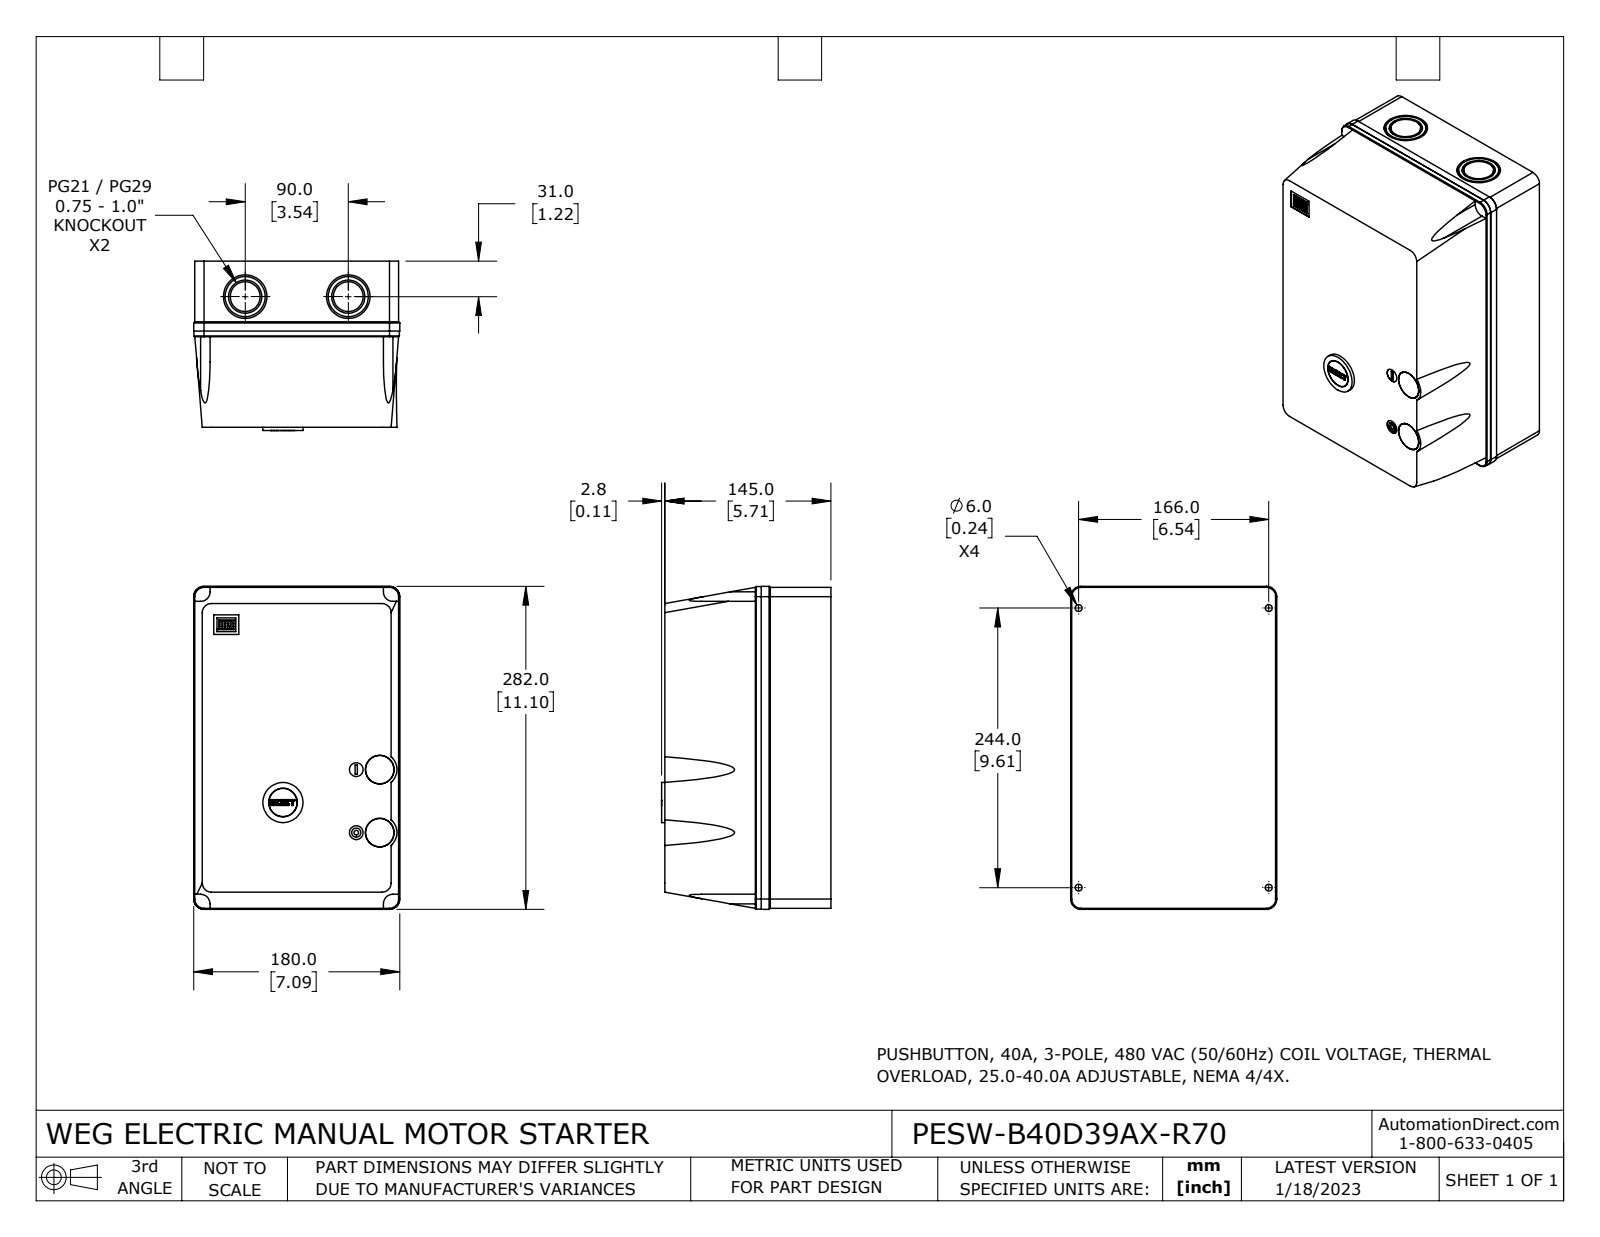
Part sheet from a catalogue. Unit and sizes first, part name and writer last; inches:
Units: inches
Overall size (bounding box): 11.102 × 7.087 × 5.823
Round holes (diameter × count): ⌀0.236 ×4, ⌀0.984 ×3, ⌀0.472 ×2, ⌀1.142 ×2, ⌀1.496 ×2, ⌀0.157 ×1, ⌀1.201 ×1
Round bosses / shafts (diameter × count): ⌀1.378 ×3, ⌀1.024 ×2, ⌀0.976 ×2, ⌀1.193 ×1, ⌀0.969 ×1, ⌀0.551 ×1, ⌀0.315 ×1
Partial cylindrical surfaces — rounded edges, fillets, slot ends (radius × count): R0.004 ×34, R0.315 ×4, R0.327 ×4, R0.343 ×4, R0.354 ×4, R0.063 ×1
Main face-to-face distances: 5.709, 7.008, 11.024, 0.039, 0.028, 7.047, 7.075, 7.035, 11.063, 7.087
Hole centre spacings: 0.807, 2.165, 2.311, 6.535, 9.606, 11.619, 1.935, 2.25
Volume: 428 in³ · Surface area: 360 in²
Bodies: 3 solids, 286 faces (130 planar, 144 cylindrical, 12 other)
Part name (STEP PRODUCT): PESW-B40D39AX-R70
STEP written by: SolidWorks 2021 (CONFIG_CONTROL_DESIGN)
